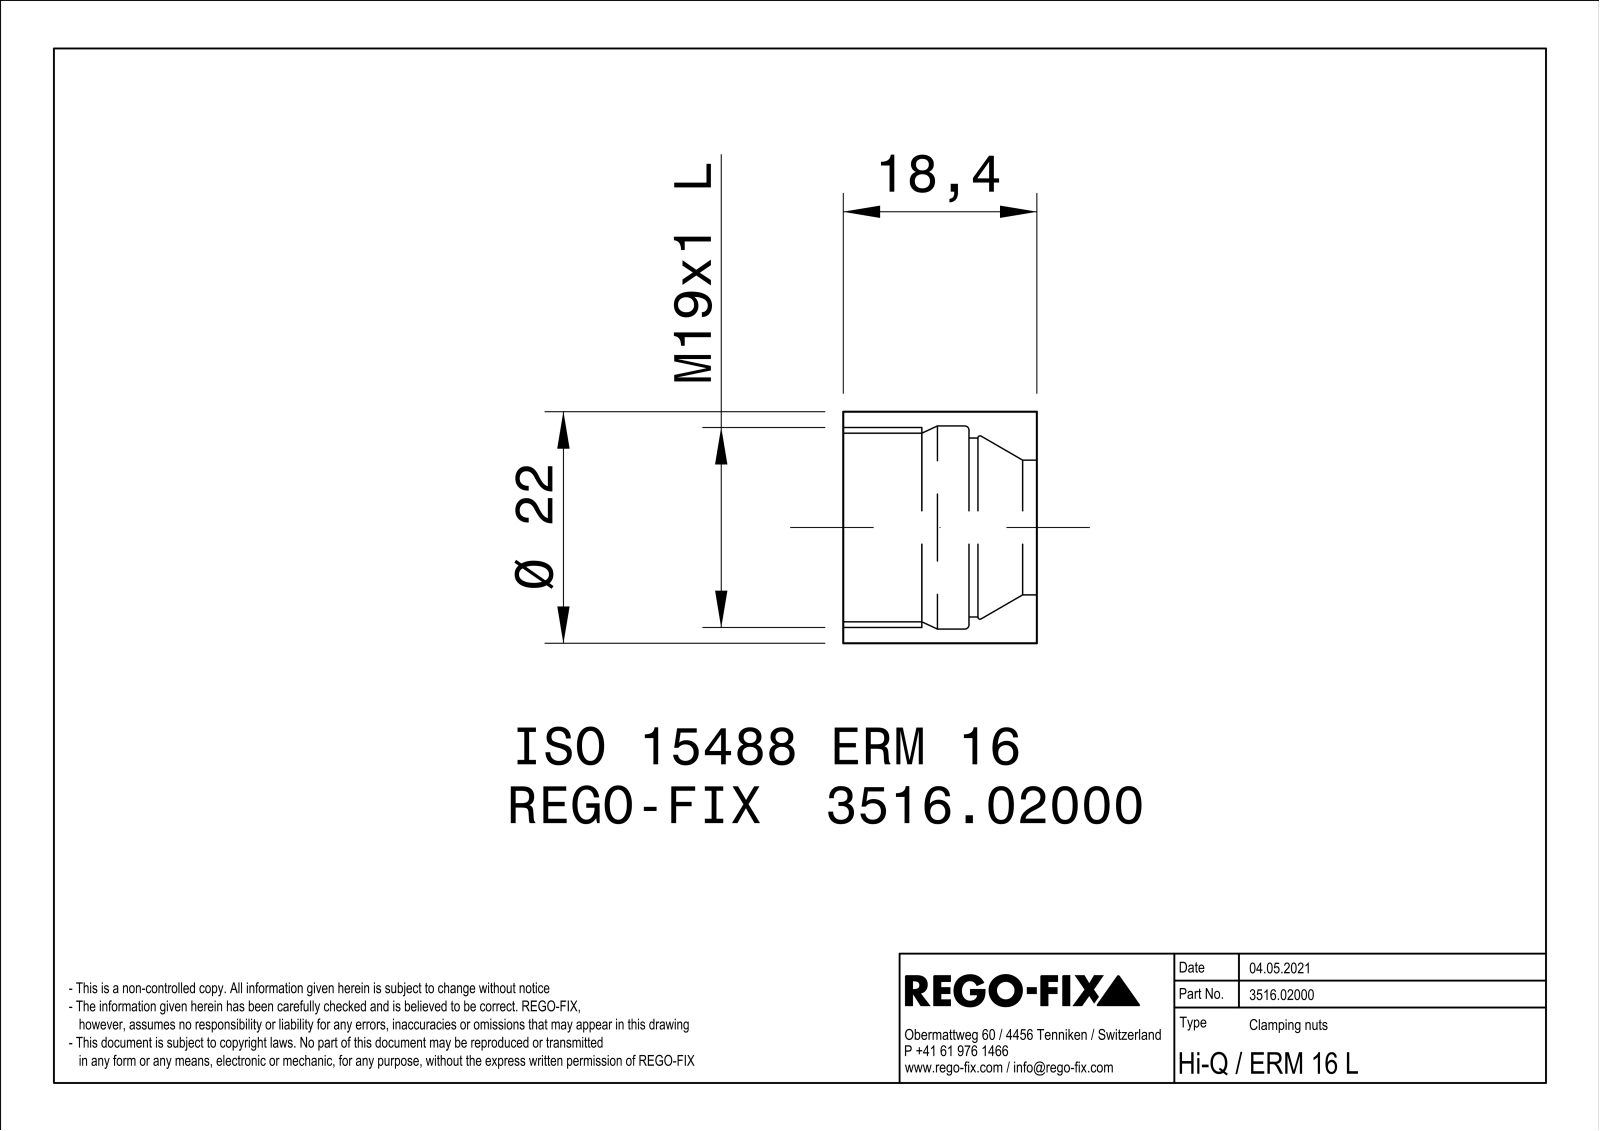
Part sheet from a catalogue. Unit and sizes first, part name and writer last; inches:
Units: inches
Overall size (bounding box): 0.866 × 0.866 × 0.724
Round holes (diameter × count): ⌀0.504 ×1, ⌀0.669 ×1, ⌀0.706 ×1, ⌀0.76 ×1
Round bosses / shafts (diameter × count): ⌀0.866 ×1
Main face-to-face distances: 0.724, 0.157, 0.254, 0.47, 0.22, 0.033, 0.504
Volume: 0.15 in³ · Surface area: 4.27 in²
Bodies: 1 solid, 42 faces (22 planar, 6 cylindrical, 14 other)
Part name (STEP PRODUCT): NOCUT
STEP written by: SIEMENS PLM Software Solid Edge ST10 (AUTOMOTIVE_DESIGN)
